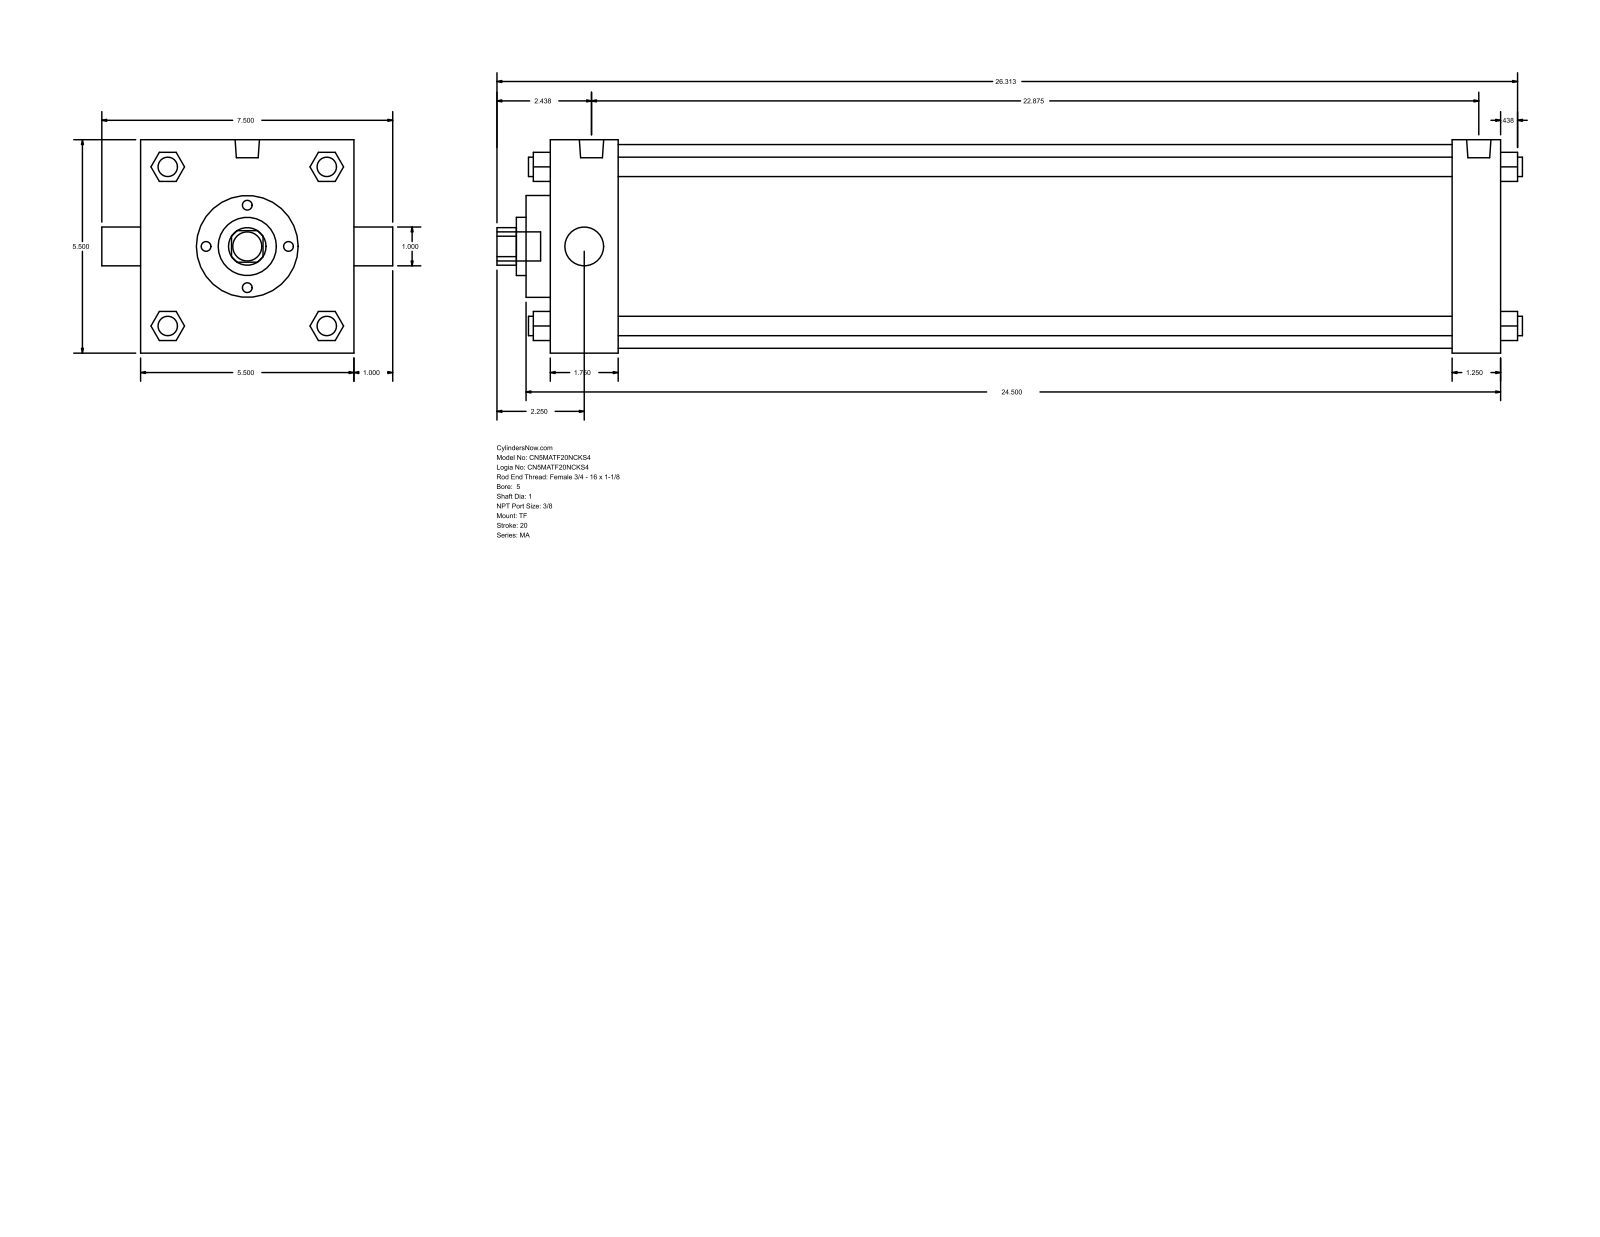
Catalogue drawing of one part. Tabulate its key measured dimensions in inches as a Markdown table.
| quantity | value |
| --- | --- |
| part name | MA_TF__0500_1 |
| STEP written by | GSSL Pune (CONFIG_CONTROL_DESIGN) |
| units | inches |
| bodies | 0 solids, 122 faces (93 planar, 29 cylindrical, 0 other) |
| overall size | 26.437 × 7.5 × 5.5 |
| round holes (diameter × count) | 1 × 2, 1.5 × 1, 2.625 × 1, 5.25 × 1 |
| round bosses / shafts (diameter × count) | 0.5 × 4, 0.437 × 3, 0.627 × 2, 0.75 × 1 |
| partial cylindrical surfaces (radius × count) | 0.484 × 1 |
| main face-to-face distances | 5.5, 24.5, 23.25, 1.25, 1.75, 21.5, 22.75, 0.625, 2.375, 23.875 |
